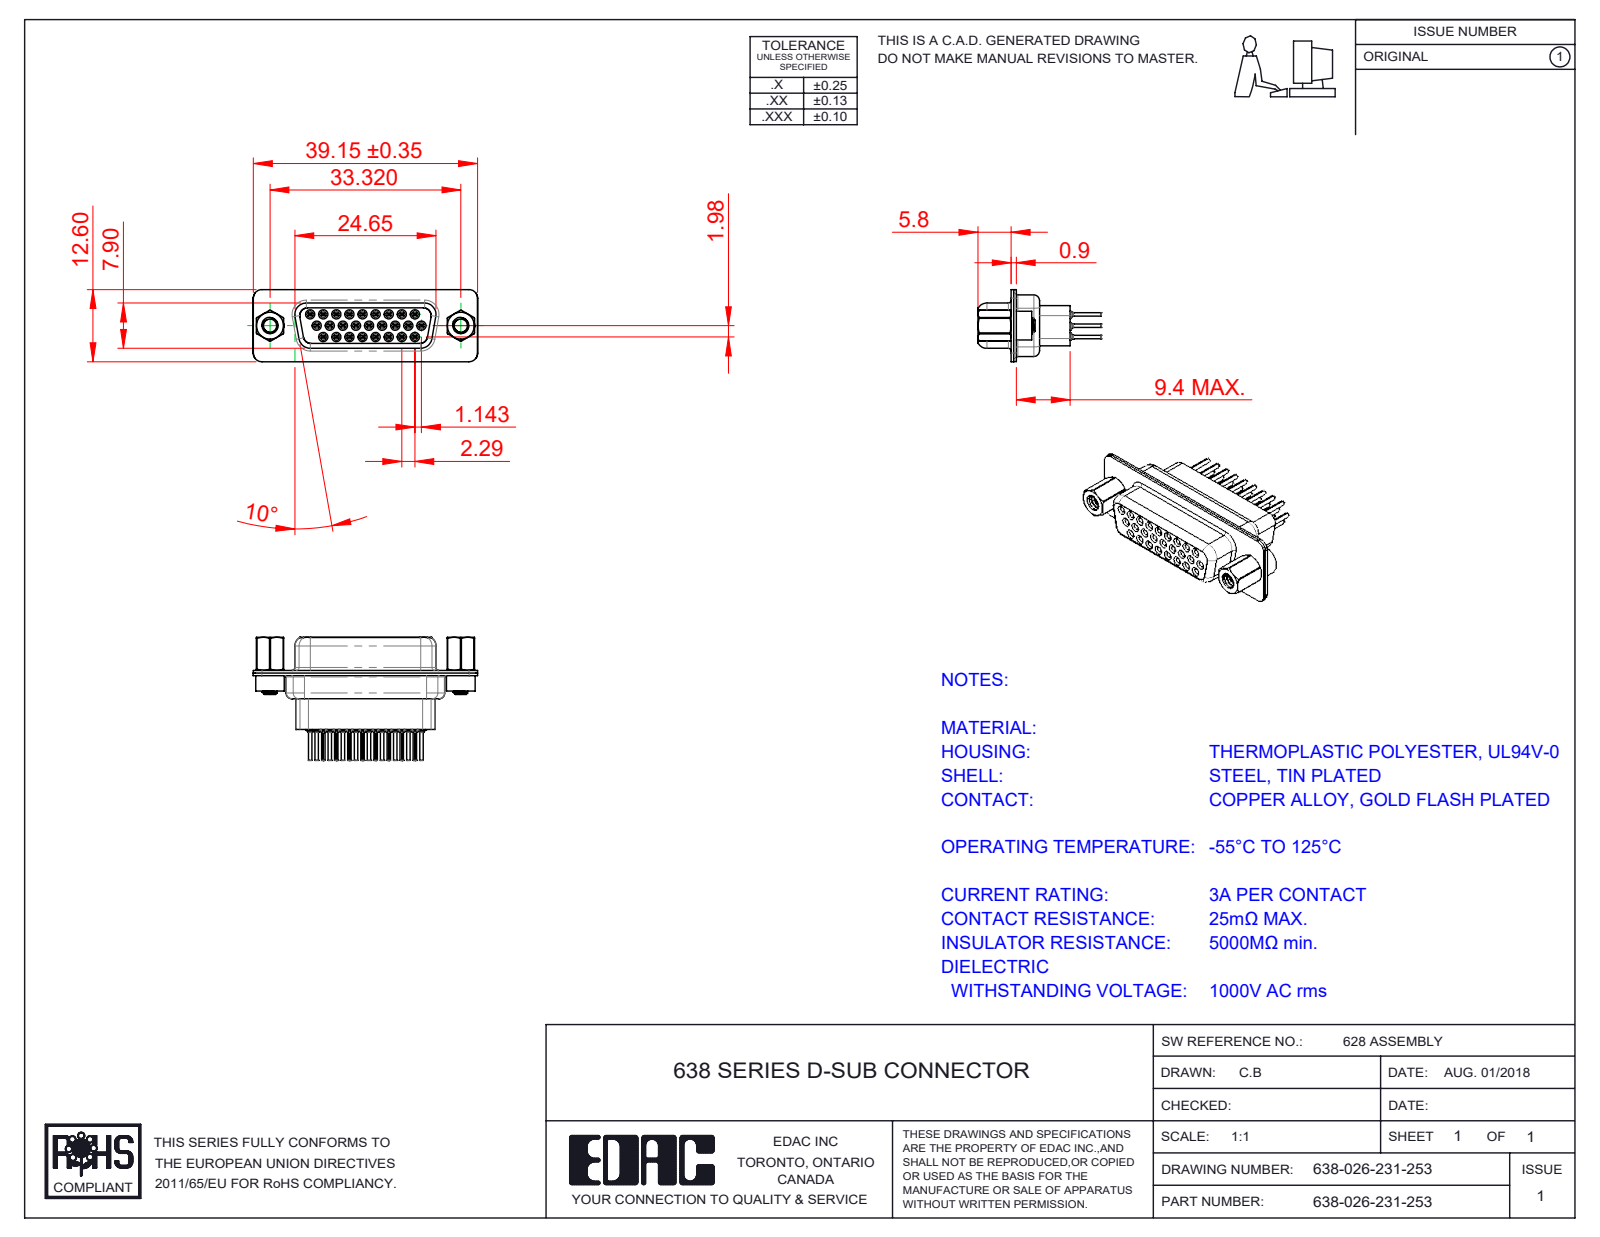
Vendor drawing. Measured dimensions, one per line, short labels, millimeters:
name: 638-026-231-253; 638 4-40 Threaded Rivet; 638 Housing_26 Contacts HP; 638 Shell Rear_26 Contacts (+5 more)
written by: SolidWorks 2020 (CONFIG_CONTROL_DESIGN)
unit: mm
bodies: 33 solids, 3603 faces (895 planar, 1067 cylindrical, 1641 other)
size: 39.19 × 21.5 × 12.6
volume: 2 889 mm³; area: 10 355 mm²
holes: 26× ⌀0.2, 26× ⌀0.8, 26× ⌀1, 26× ⌀1.1, 26× ⌀1.6, 26× ⌀1.7, 26× ⌀1.8, 2× ⌀2.26, 2× ⌀2.29, 2× ⌀4, 2× ⌀4.05, 2× ⌀4.85
bosses: 26× ⌀2, 26× ⌀1.5, 26× ⌀1.2, 26× ⌀0.6, 2× ⌀5, 2× ⌀4.95, 2× ⌀4.8, 2× ⌀2.79
rounds: 52× R0.1, 20× R1.5, 18× R0.28, 12× R2, 8× R1.55, 5× R1.35, 4× R0.25, 4× R0.5
face distances: 0.45, 0.4, 0.9, 6.6, 1.43, 8.88, 7, 2.28, 5.8, 9.4
hole spacings: 3.96, 2.28, 4.57, 6.05, 2.29, 8.24, 6.86, 10.48
